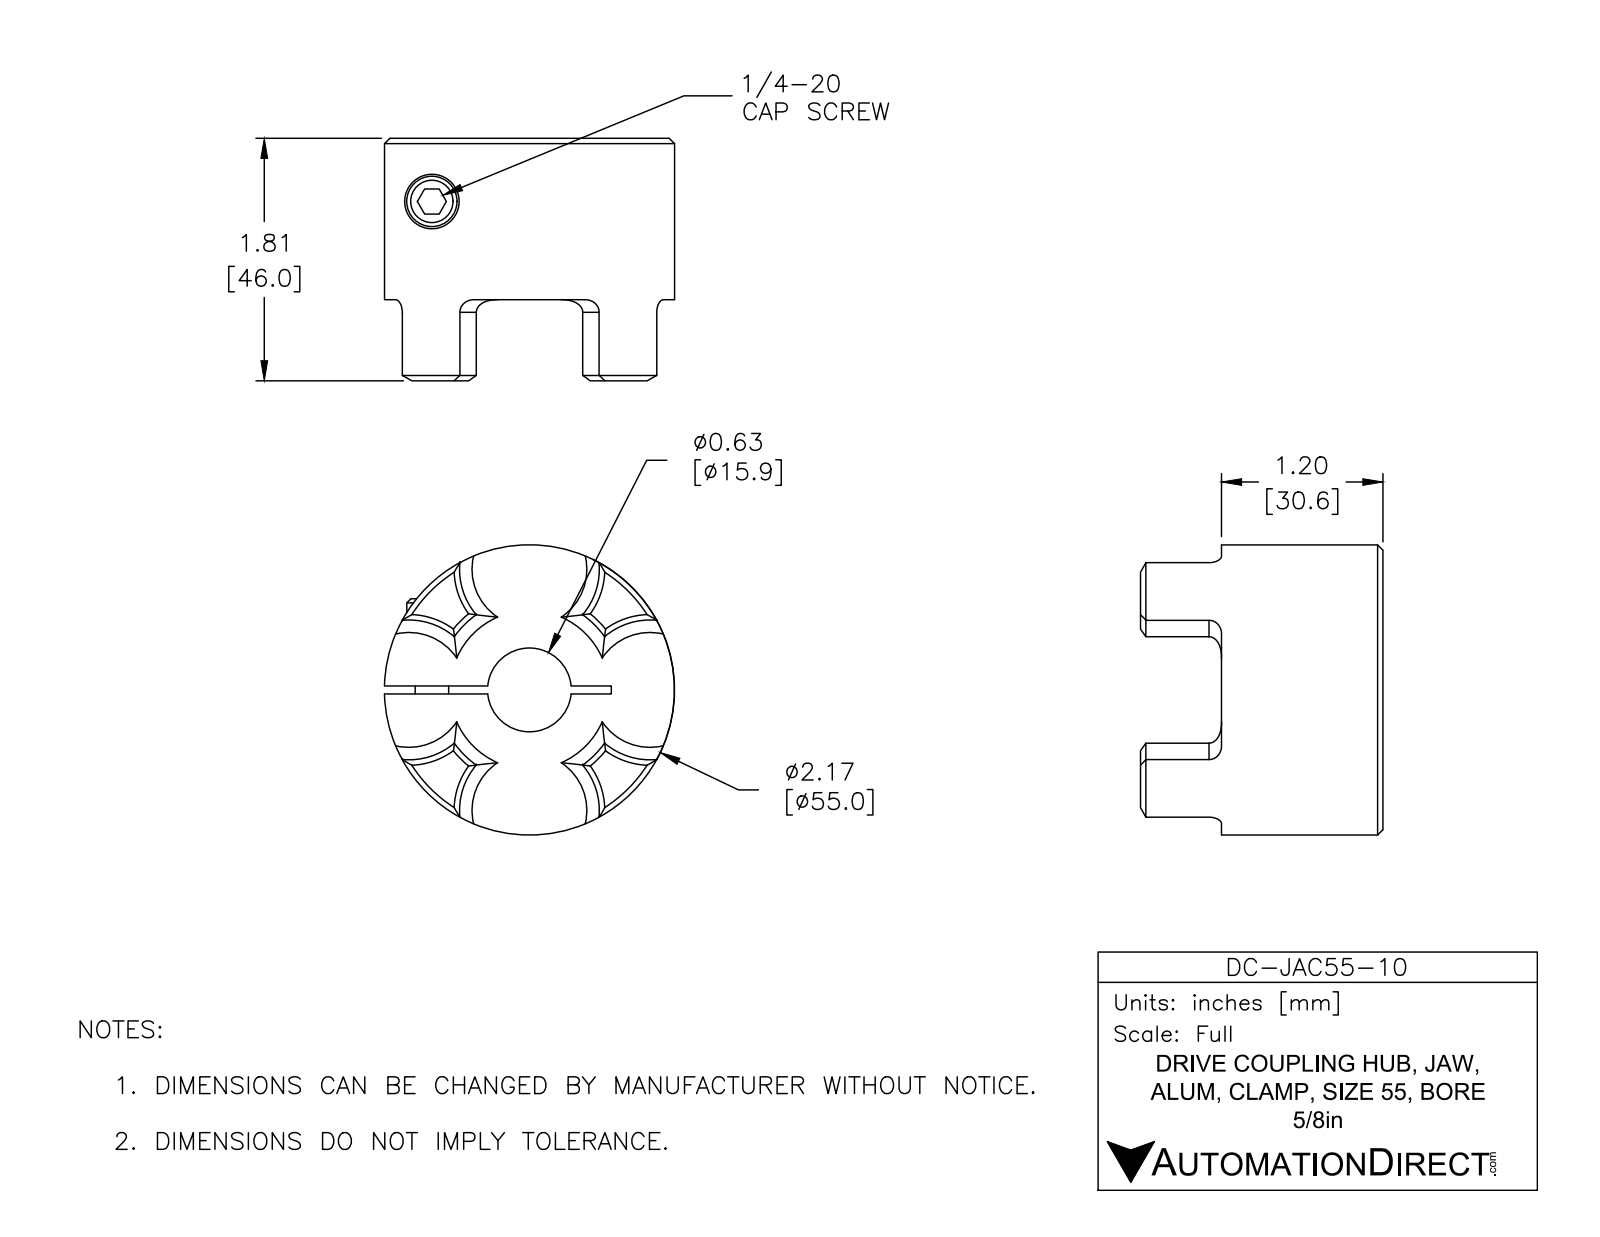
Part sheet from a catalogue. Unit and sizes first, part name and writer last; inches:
Units: inches
Overall size (bounding box): 2.19 × 2.165 × 1.81
Round holes (diameter × count): ⌀0.266 ×1, ⌀0.406 ×1, ⌀0.625 ×1
Round bosses / shafts (diameter × count): ⌀2.165 ×1, ⌀0.375 ×1, ⌀0.25 ×1
Partial cylindrical surfaces — rounded edges, fillets, slot ends (radius × count): R0.522 ×4, R0.687 ×1
Main face-to-face distances: 1.205, 0.06, 1.81, 0.605, 0.46, 0.4, 0.187, 0.29, 0.35, 0.75
Volume: 4.285 in³ · Surface area: 25.5 in²
Bodies: 2 solids, 92 faces (22 planar, 29 cylindrical, 41 other)
Part name (STEP PRODUCT): DC-JA55-10_POST2016
STEP written by: SolidWorks 2016 (AUTOMOTIVE_DESIGN)
